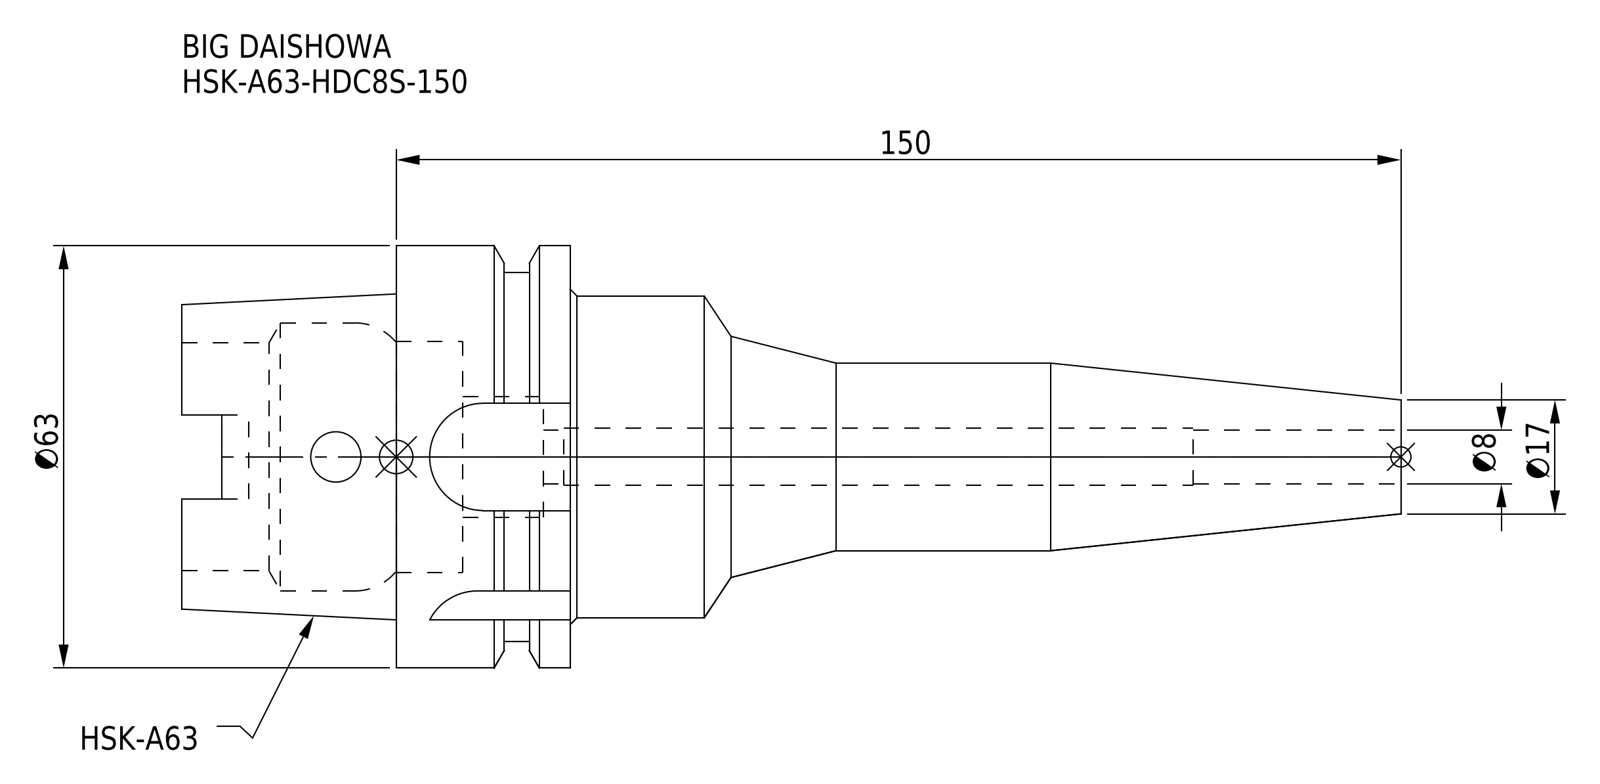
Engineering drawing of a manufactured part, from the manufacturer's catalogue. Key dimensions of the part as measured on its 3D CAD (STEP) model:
Part name (STEP PRODUCT): HSK-A63-HDC8S-150
STEP written by: CREO PARAMETRIC BY PTC INC, 2016380 (AUTOMOTIVE_DESIGN)
Units: millimetres
Bodies: 1 solid, 99 faces (38 planar, 39 cylindrical, 22 other)
Overall size (bounding box): 182 × 63 × 63
Volume: 170 204 mm³ · Surface area: 36 053 mm²
Round holes (diameter × count): ⌀7.5 ×1, ⌀8 ×1, ⌀8.5 ×1, ⌀18 ×1, ⌀34 ×1, ⌀34.5 ×1, ⌀40 ×1
Round bosses / shafts (diameter × count): ⌀63 ×1, ⌀55 ×1, ⌀48 ×1, ⌀28 ×1
Partial cylindrical surfaces — rounded edges, fillets, slot ends (radius × count): R2.88 ×4, R8 ×4
Main face-to-face distances: 26, 16.05, 9.95, 58, 41.95, 32, 53, 12, 4.05, 21.95
